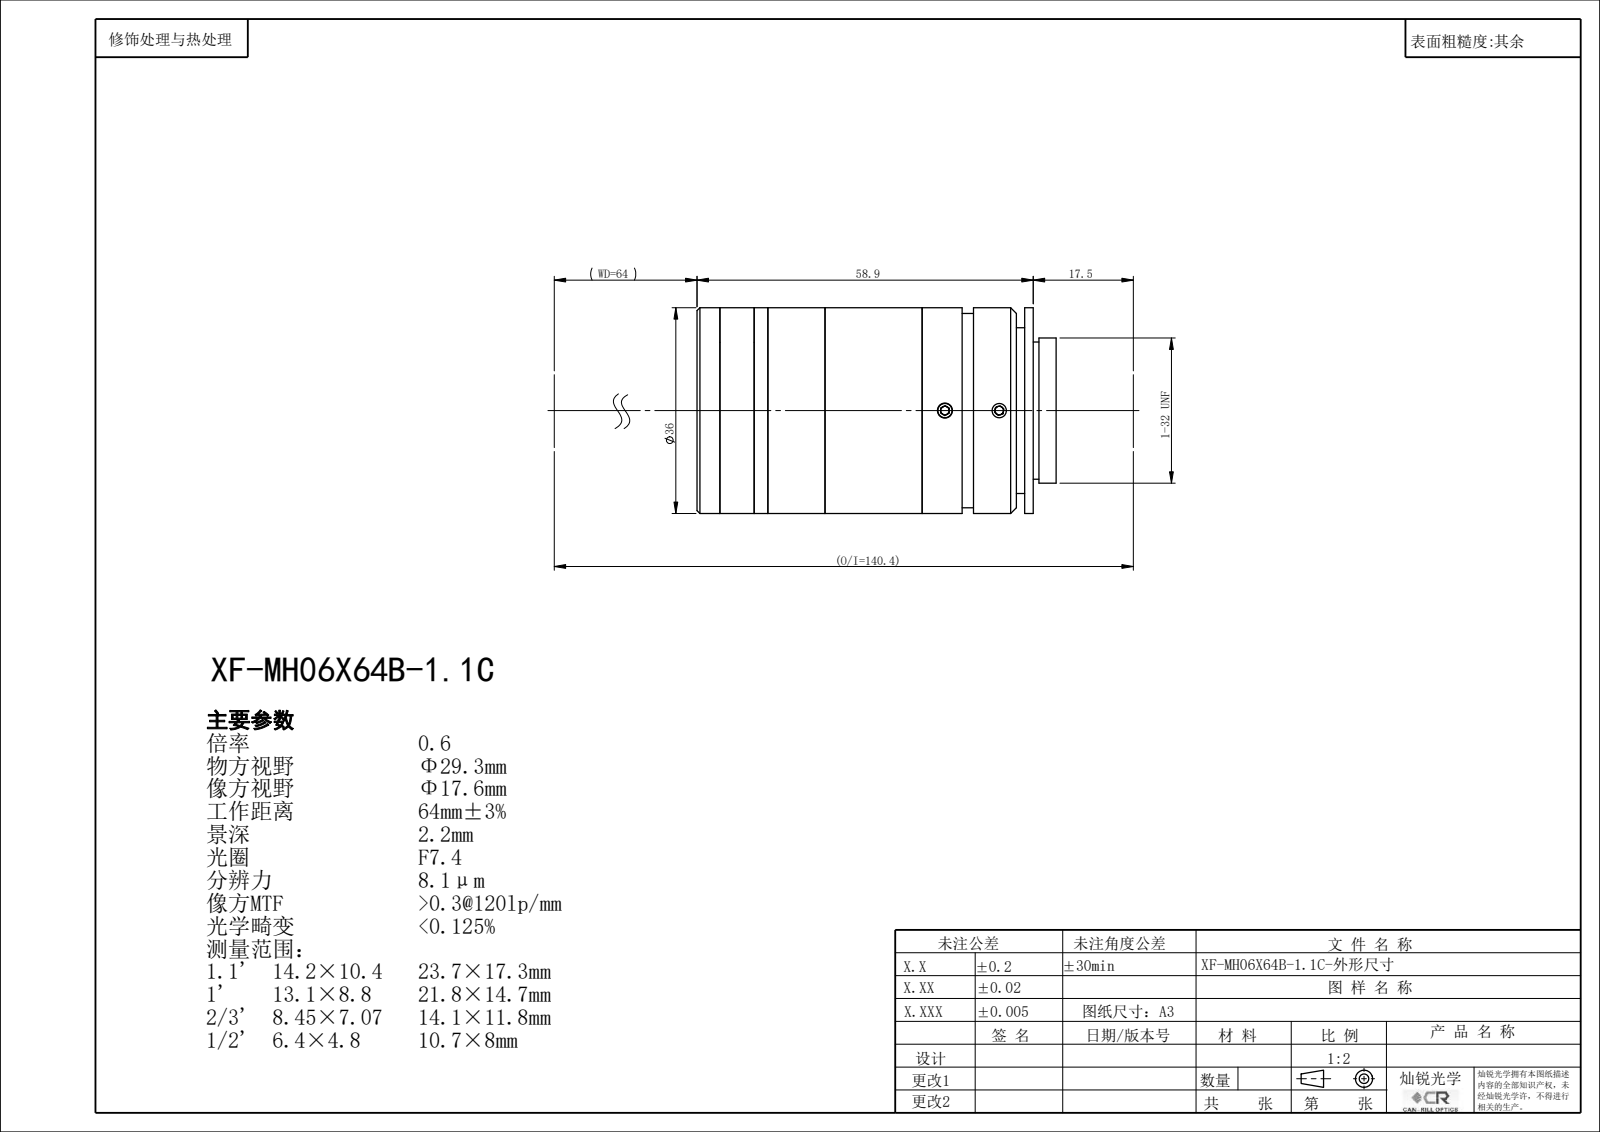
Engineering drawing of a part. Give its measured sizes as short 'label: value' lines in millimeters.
name: XF-MH06X64B-1.1C
written by: SolidWorks 2022 (CONFIG_CONTROL_DESIGN)
unit: mm
bodies: 0 solids, 143 faces (74 planar, 42 cylindrical, 27 other)
size: 62.86 × 36 × 36
holes: 3× ⌀2.5, 1× ⌀14, 1× ⌀16.4, 1× ⌀22.4, 1× ⌀24, 1× ⌀24.9, 1× ⌀26, 1× ⌀26.4
bosses: 1× ⌀36, 1× ⌀34, 1× ⌀25.4
face distances: 19.46, 58.86, 39.4, 1.5, 57.36, 17.96, 12.4, 10, 52.86, 27
